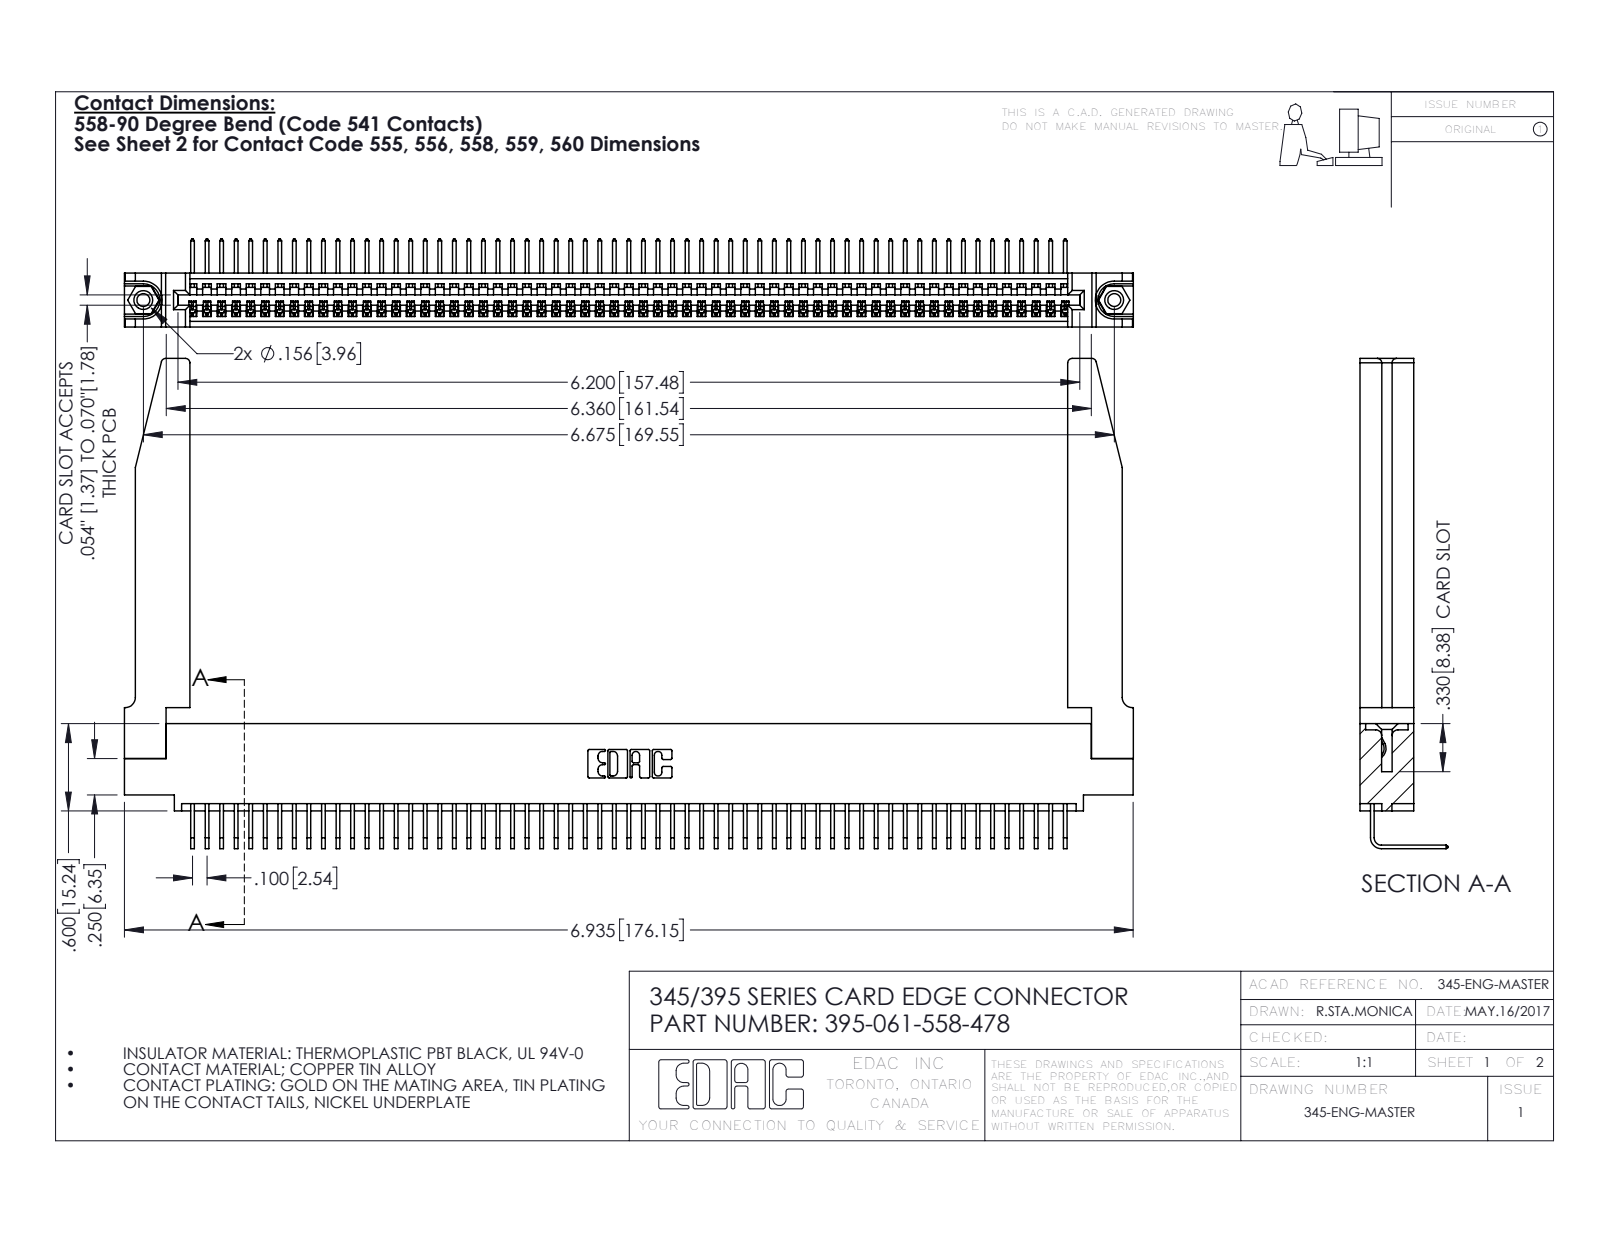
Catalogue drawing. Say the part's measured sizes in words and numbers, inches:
The part is named "345-220-078_345-220-078; 345-250-001_345-250-001-102; 395-061-558-478; 345 Part_0.110 Offset - 0.156 Dia-TH (+1 more)". Its 3-D file was written by "SolidWorks 2016 (CONFIG_CONTROL_DESIGN)". It is 66 solids with 4024 faces: 2788 planar, 1184 cylindrical and 52 other. Overall it measures 6.936 by 3.369 by 0.605 inches. Its volume is 1.513 cubic inches and its surface area 48.04 square inches. Round holes: 2 of diameter 0.089, 2 of diameter 0.125, 2 of diameter 0.156, 1 of diameter 0.064. Round bosses or shafts: 2 of diameter 0.155. Partial cylindrical surfaces (rounded edges, fillets, slot ends): 122 of radius 0.006, 22 of radius 0.01, 8 of radius 0.03, 6 of radius 0.007, 6 of radius 0.031, 3 of radius 0.026, 2 of radius 0.031, 2 of radius 0.04. The main face-to-face distances are 0.072, 0.37, 0.298, 0.098, 0.272, 0.025, 0.2, 0.225, 0.148, 0.15. The hole center spacings are 0.27, 6.439, 6.675.
